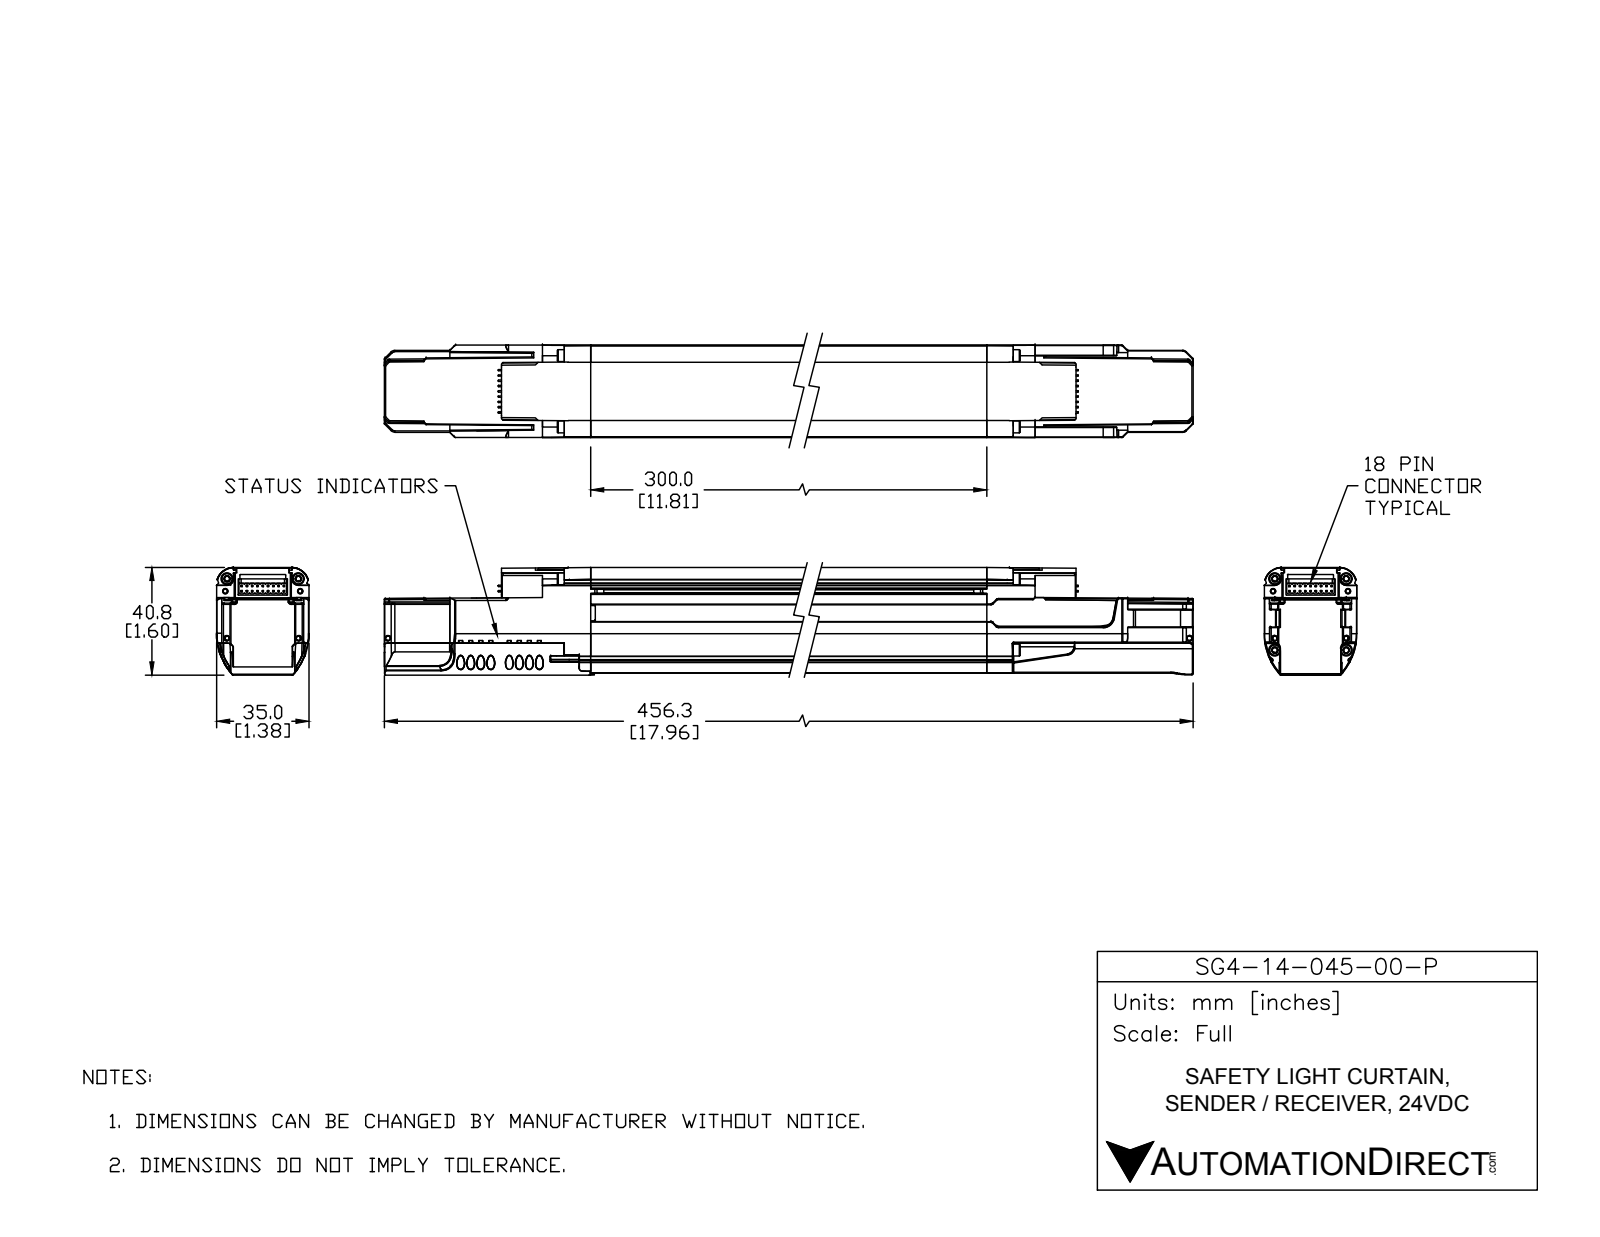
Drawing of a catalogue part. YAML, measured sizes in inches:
part_name: "SG4-14-045-00-P"
step_written_by: "SolidWorks 2017 (AUTOMOTIVE_DESIGN)"
units: inches
bodies: {solids: 16, faces: 534, planar: 362, cylindrical: 110, other: 62}
overall_size: [17.963, 2.58, 2.023]
volume: 32.97
surface_area: 199.3
round_holes:
  - {diameter: 0.07, count: 6}
  - {diameter: 0.1, count: 4}
  - {diameter: 0.165, count: 4}
  - {diameter: 0.209, count: 4}
  - {diameter: 0.26, count: 4}
  - {diameter: 0.065, count: 1}
  - {diameter: 0.065, count: 1}
round_bosses_or_shafts:
  - {diameter: 0.394, count: 4}
  - {diameter: 0.197, count: 4}
partial_cylinders:
  - {radius: 0.106, count: 16}
  - {radius: 0.118, count: 8}
  - {radius: 0.1, count: 4}
  - {radius: 0.11, count: 4}
  - {radius: 0.08, count: 2}
  - {radius: 0.12, count: 2}
  - {radius: 0.123, count: 2}
  - {radius: 0.125, count: 2}
face_to_face_distances: [0.06, 0.084, 0.024, 1.49, 1.466, 1.55, 1.057, 0.118, 0.481, 0.985]
hole_center_spacings: [0.569, 10.22, 0.02, 0.204, 0.207, 0.207, 0.227, 0.71]
